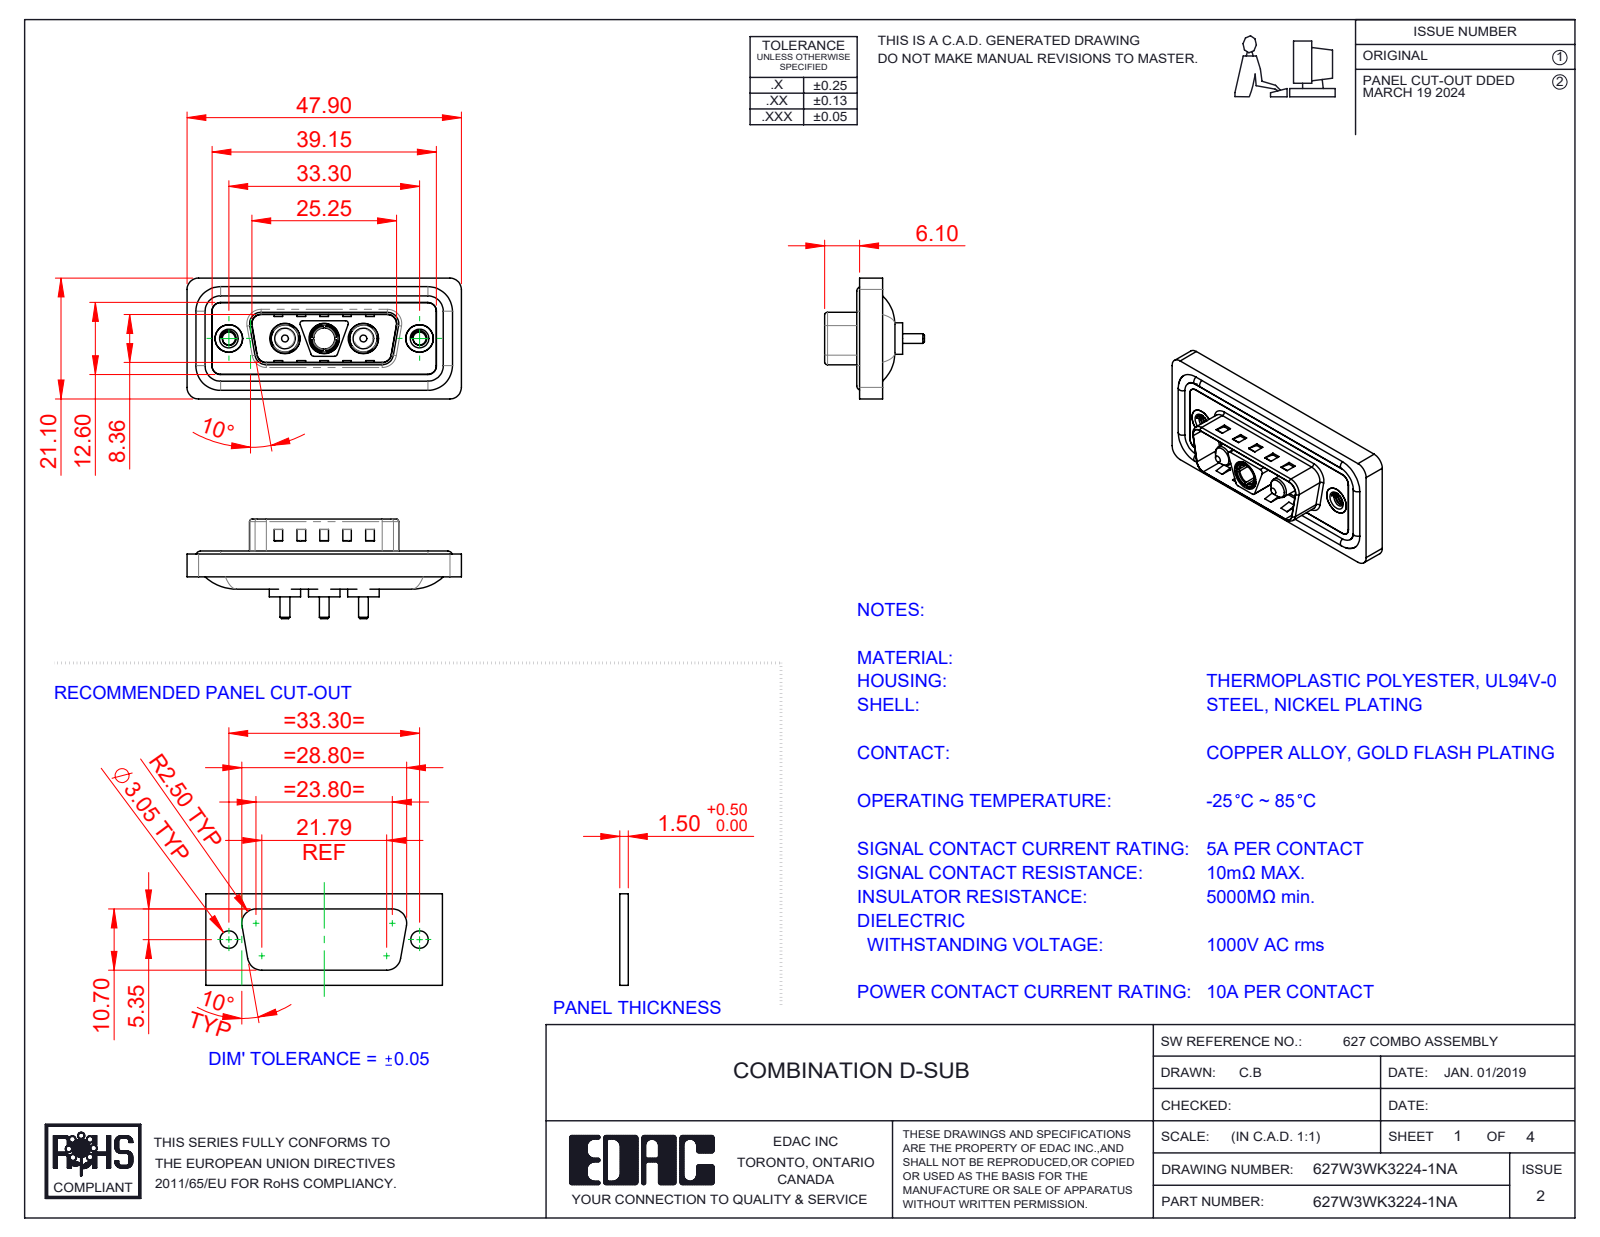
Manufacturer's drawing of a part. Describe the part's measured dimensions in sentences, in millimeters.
The part is named "627Combo Shell Front_15 Contacts; Power Socket_10A S; 627W3WK3224-1NA; 627Combo Shell Rear_15 Contacts (+4 more)". Its 3-D file was written by "SolidWorks 2023 (CONFIG_CONTROL_DESIGN)". It is 13 solids with 607 faces: 231 planar, 252 cylindrical and 124 other. Overall it measures 47.9 by 21.1 by 17.4 millimeters. Its volume is 5 646 cubic millimeters and its surface area 9 087 square millimeters. Round holes: 3 of diameter 4.85, 3 of diameter 5.3, 2 of diameter 2.26, 2 of diameter 4, 2 of diameter 4.8, 2 of diameter 5, 1 of diameter 3.7. Round bosses or shafts: 4 of diameter 1.6, 3 of diameter 5.5, 3 of diameter 5.2, 3 of diameter 4.75, 3 of diameter 3.75, 3 of diameter 1.7, 2 of diameter 4.9, 2 of diameter 3.6. Partial cylindrical surfaces (rounded edges, fillets, slot ends): 26 of radius 1.5, 20 of radius 2, 12 of radius 0.5, 8 of radius 1.6, 4 of radius 0.25, 4 of radius 0.6, 4 of radius 0.65, 4 of radius 0.9. The main face-to-face distances are 0.4, 1.5, 1.1, 0.5, 1.6, 3.1, 2.9, 4, 0.82, 9.58. The hole center spacings are 6.85, 9.8, 16.65, 23.5, 13.7, 33.3.
